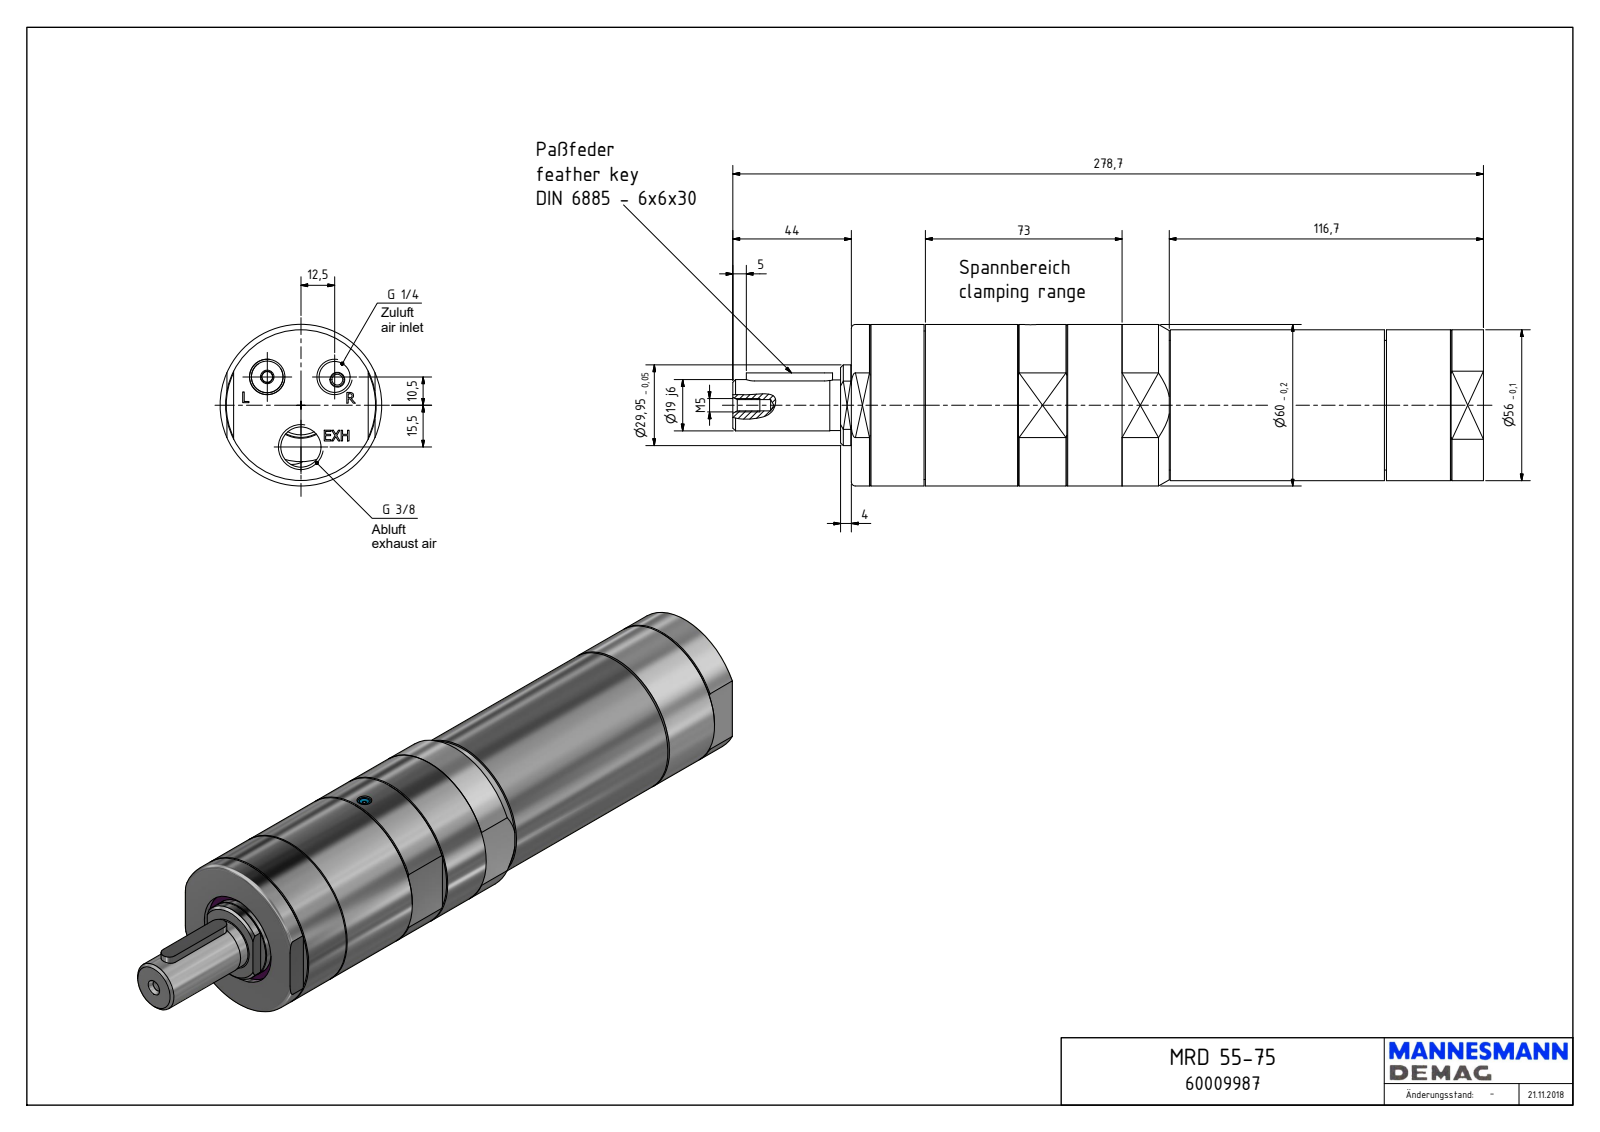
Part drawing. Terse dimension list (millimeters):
name: MRD 55-75_60009987
written by: Autodesk Inventor 2018 (AUTOMOTIVE_DESIGN)
unit: mm
bodies: 1 solid, 226 faces (127 planar, 47 cylindrical, 52 other)
size: 278.7 × 60 × 60
volume: 624 163 mm³; area: 59 841 mm²
holes: 2× ⌀4, 1× ⌀1.55, 1× ⌀4.13, 1× ⌀5.5, 1× ⌀11.45, 1× ⌀14.95, 1× ⌀35, 1× ⌀36.5, 1× ⌀40, 1× ⌀48.38, 1× ⌀55.38
bosses: 1× ⌀60, 1× ⌀56, 1× ⌀55.18, 1× ⌀48.18, 1× ⌀29.95, 1× ⌀19, 1× ⌀18.8, 1× ⌀5
rounds: 2× R3, 2× R6, 1× R5.72, 1× R19.49, 1× R23, 1× R25.76
face distances: 234.7, 55, 2.5, 52.5, 197.9, 36.8, 118.4, 79.5, 116.3, 0.8
hole spacings: 16.32, 28.85, 15.5, 25
